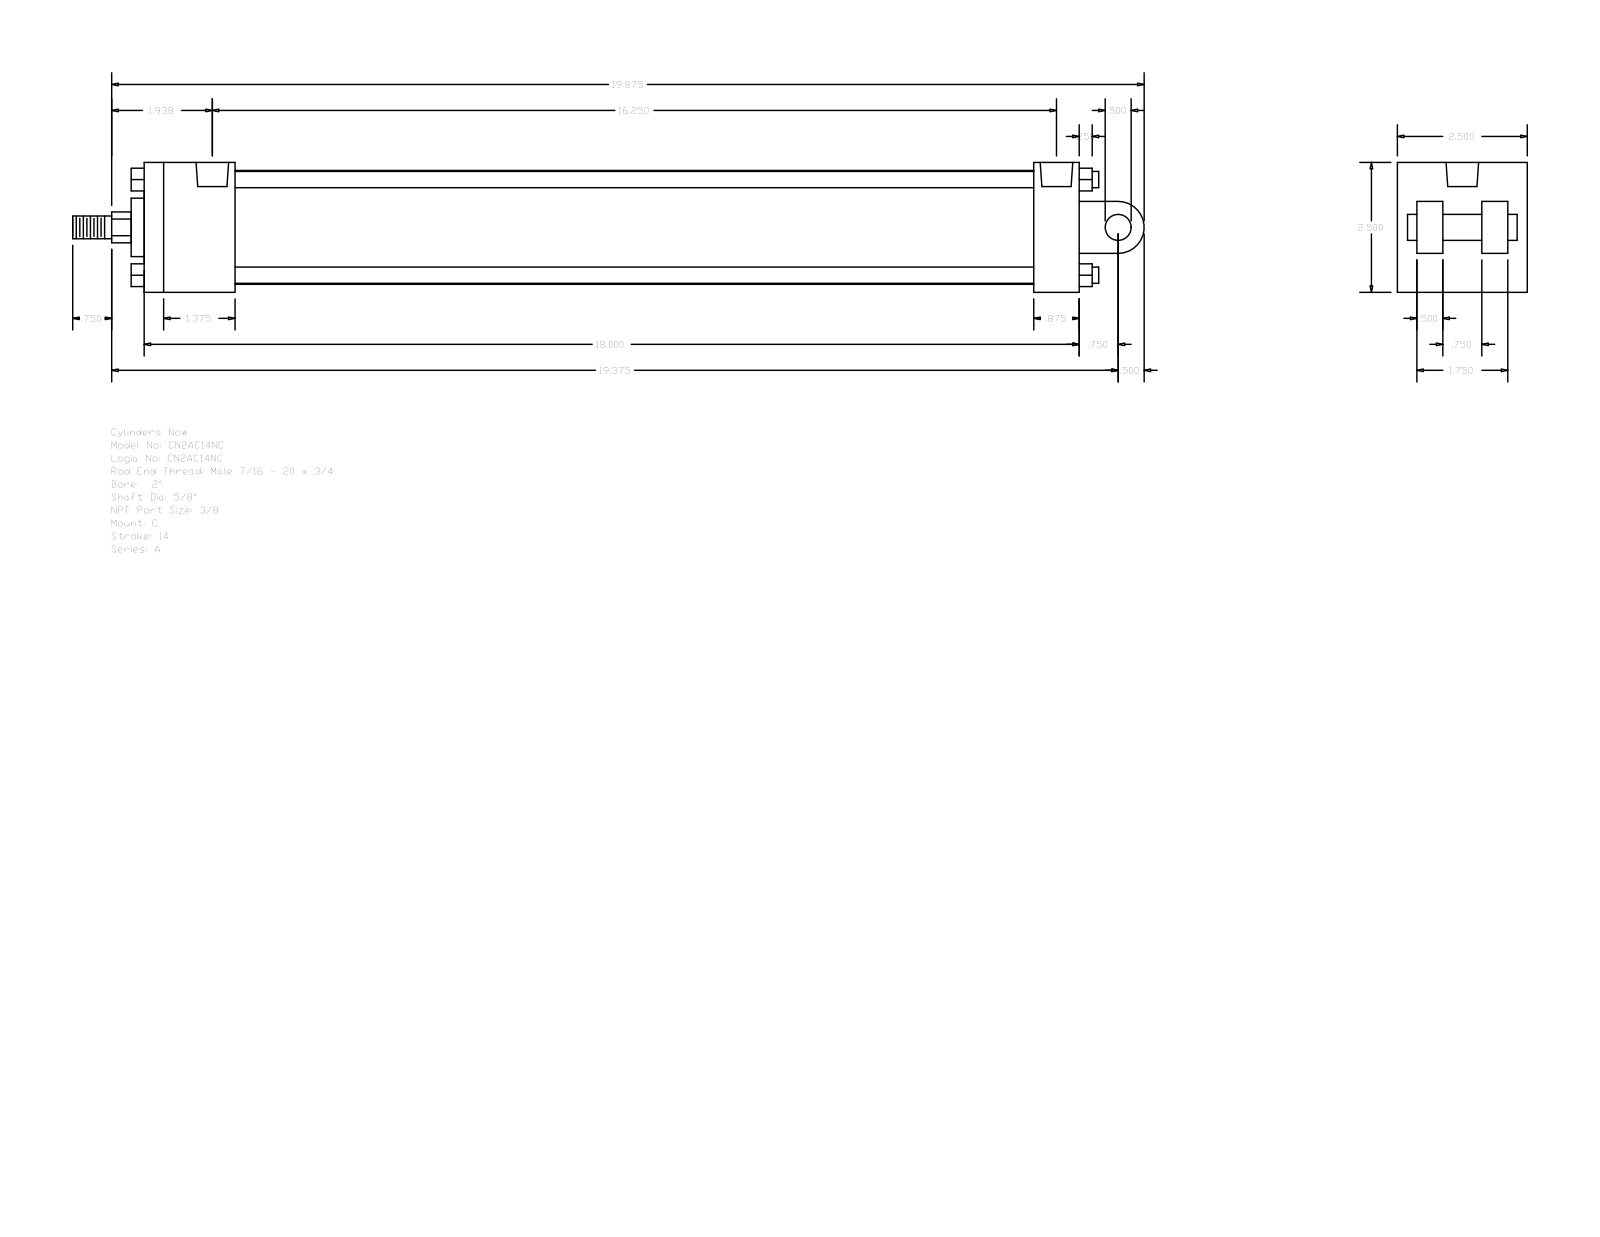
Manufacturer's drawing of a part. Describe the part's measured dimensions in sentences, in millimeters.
The part is named "A_C__0200_0.625". Its 3-D file was written by "GSSL Pune (CONFIG_CONTROL_DESIGN)". It is 0 solids with 135 faces: 102 planar, 33 cylindrical and 0 other. Overall it measures 523.88 by 63.5 by 63.5 millimeters. Round holes: 4 of diameter 5.56, 2 of diameter 15.93. Round bosses or shafts: 4 of diameter 7.94, 1 of diameter 55.63, 1 of diameter 28.57, 1 of diameter 15.88, 1 of diameter 12.7, 1 of diameter 11.11. Partial cylindrical surfaces (rounded edges, fillets, slot ends): 1 of radius 7.54, 1 of radius 12.7. The main face-to-face distances are 63.5, 457.19, 22.22, 44.45, 412.74, 434.97, 390.52, 12.7, 53.98, 19.05. The hole center spacings are 404.8, 3.97, 3.98, 408.77, 408.78, 412.75.
